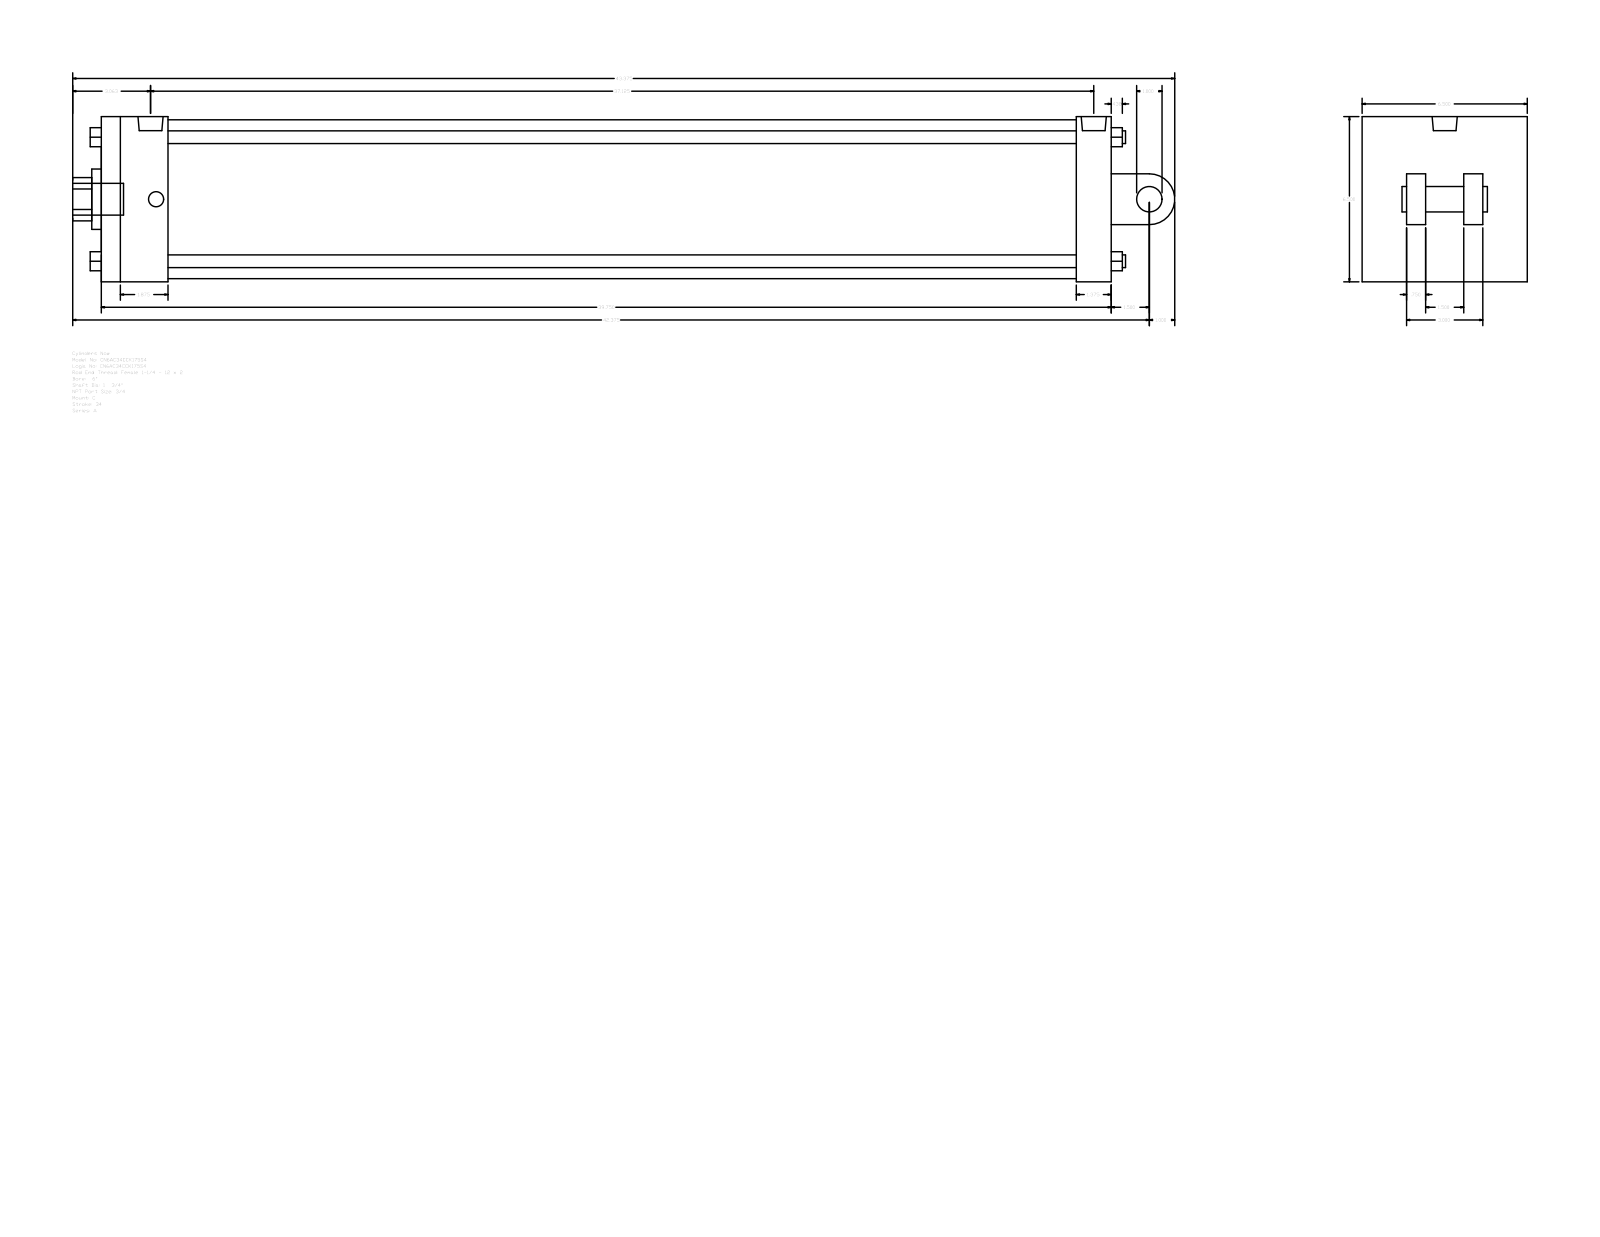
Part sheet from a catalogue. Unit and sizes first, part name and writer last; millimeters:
Units: millimetres
Overall size (bounding box): 1101.72 × 165.1 × 165.1
Round holes (diameter × count): ⌀15.08 ×2, ⌀25.12 ×1, ⌀44.45 ×1, ⌀60.33 ×1, ⌀158.75 ×1
Round bosses / shafts (diameter × count): ⌀12.7 ×4, ⌀15.08 ×2, ⌀31.75 ×1, ⌀25.4 ×1, ⌀25.12 ×1
Partial cylindrical surfaces — rounded edges, fillets, slot ends (radius × count): R21.63 ×1, R25.4 ×1
Main face-to-face distances: 165.1, 1009.65, 19.05, 57.15, 34.92, 66.68, 942.97, 974.73, 908.05, 44.45
Hole centre spacings: 5.56
Bodies: 0 solids, 135 faces (102 planar, 33 cylindrical, 0 other)
Part name (STEP PRODUCT): A_C__0600_1.75
STEP written by: GSSL Pune (CONFIG_CONTROL_DESIGN)
